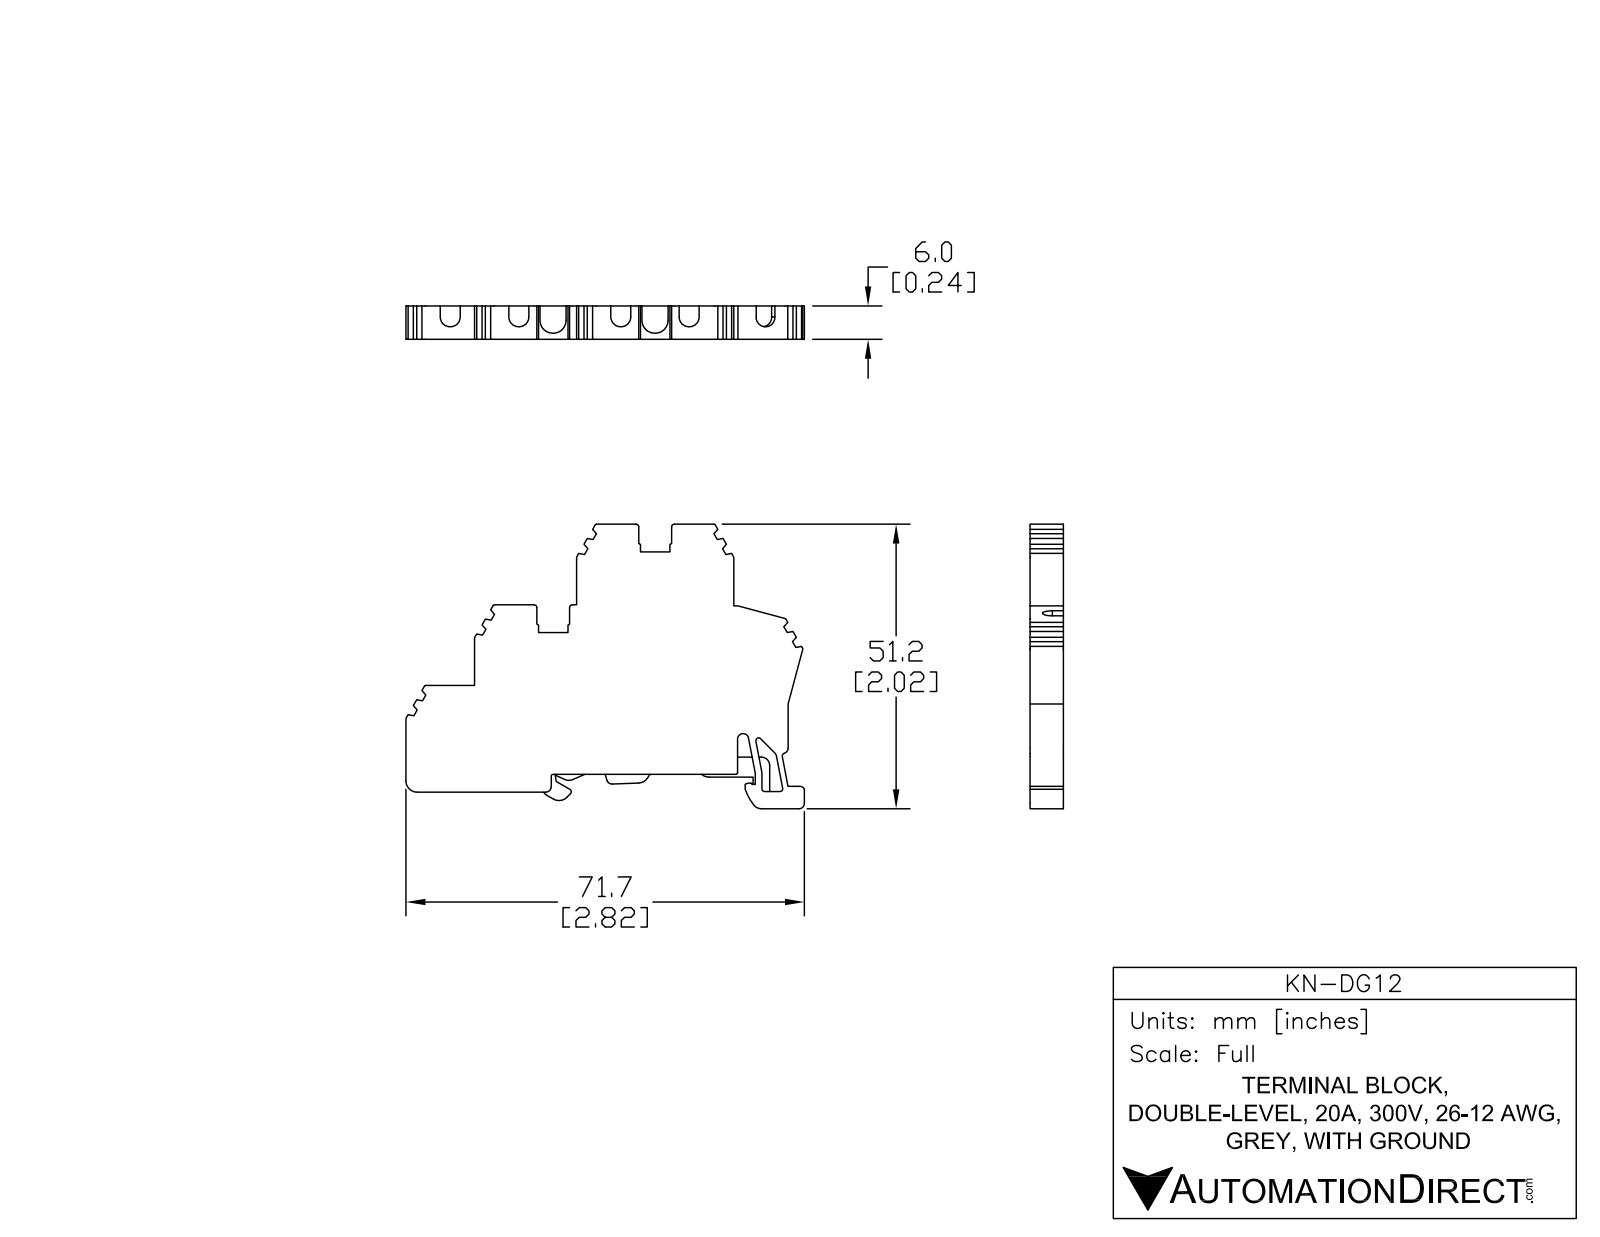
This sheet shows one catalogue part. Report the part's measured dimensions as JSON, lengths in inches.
{"part_name": "KN-DG12", "step_written_by": "SolidWorks 2014 (AUTOMOTIVE_DESIGN)", "units": "inches", "bodies": {"solids": 4, "faces": 201, "planar": 145, "cylindrical": 56, "other": 0}, "overall_size": [2.823, 2.016, 0.236], "volume_in3": 0.848, "surface_area_in2": 10.9, "partial_cylinders_radius": [[0.02, 14], [0.012, 9], [0.039, 6], [0.071, 5], [0.079, 5], [0.093, 2], [0.008, 1], [0.035, 1]], "face_to_face_distances": [0.236, 0.069, 0.167, 0.126, 0.098, 0.571, 0.722, 0.115, 0.089, 1.65]}
